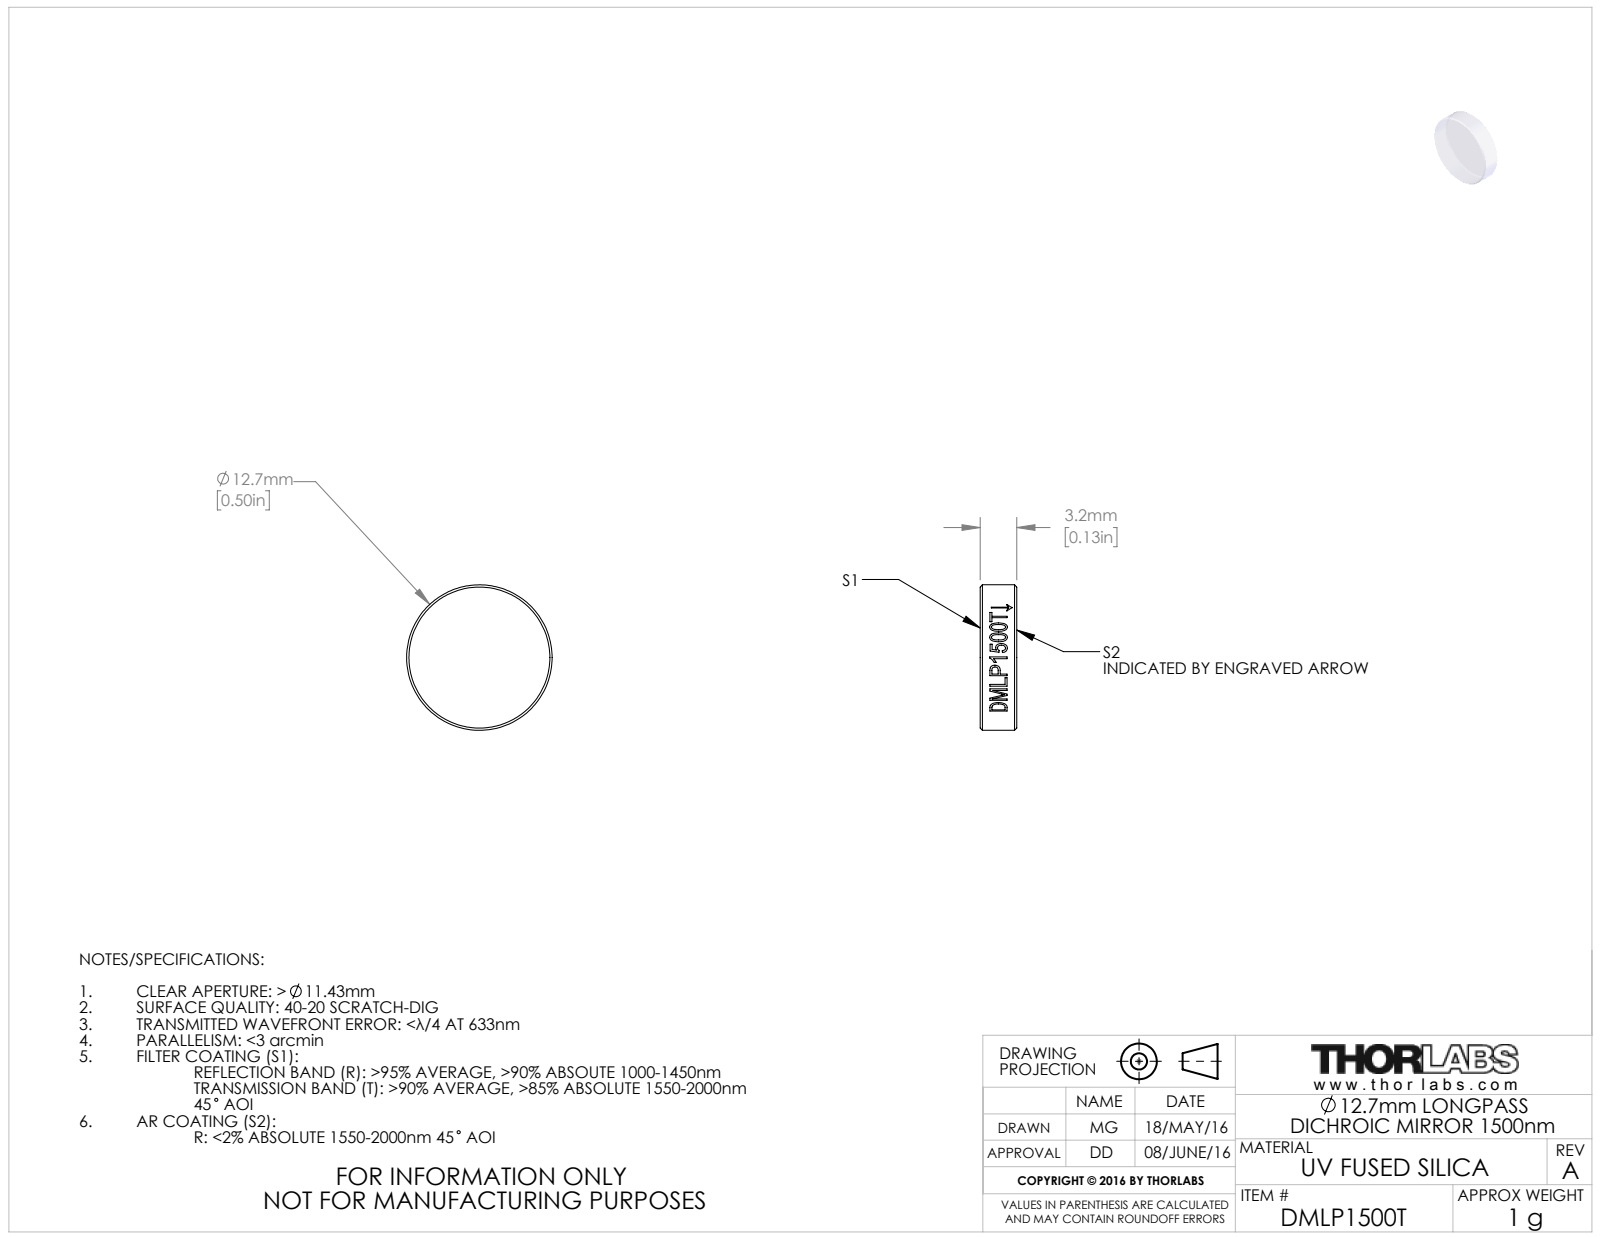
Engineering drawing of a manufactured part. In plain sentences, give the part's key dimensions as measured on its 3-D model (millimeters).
The part is named "TTN045300-E0W". Its 3-D file was written by "SolidWorks 2016 (CONFIG_CONTROL_DESIGN)". It is 1 solid with 22 faces: 2 planar, 16 cylindrical and 4 other. Overall it measures 12.7 by 12.7 by 3.2 millimeters. Its volume is 404 cubic millimeters and its surface area 372 square millimeters. Round bosses or shafts: 1 of diameter 12.7. The main face-to-face distances are 3.2.
